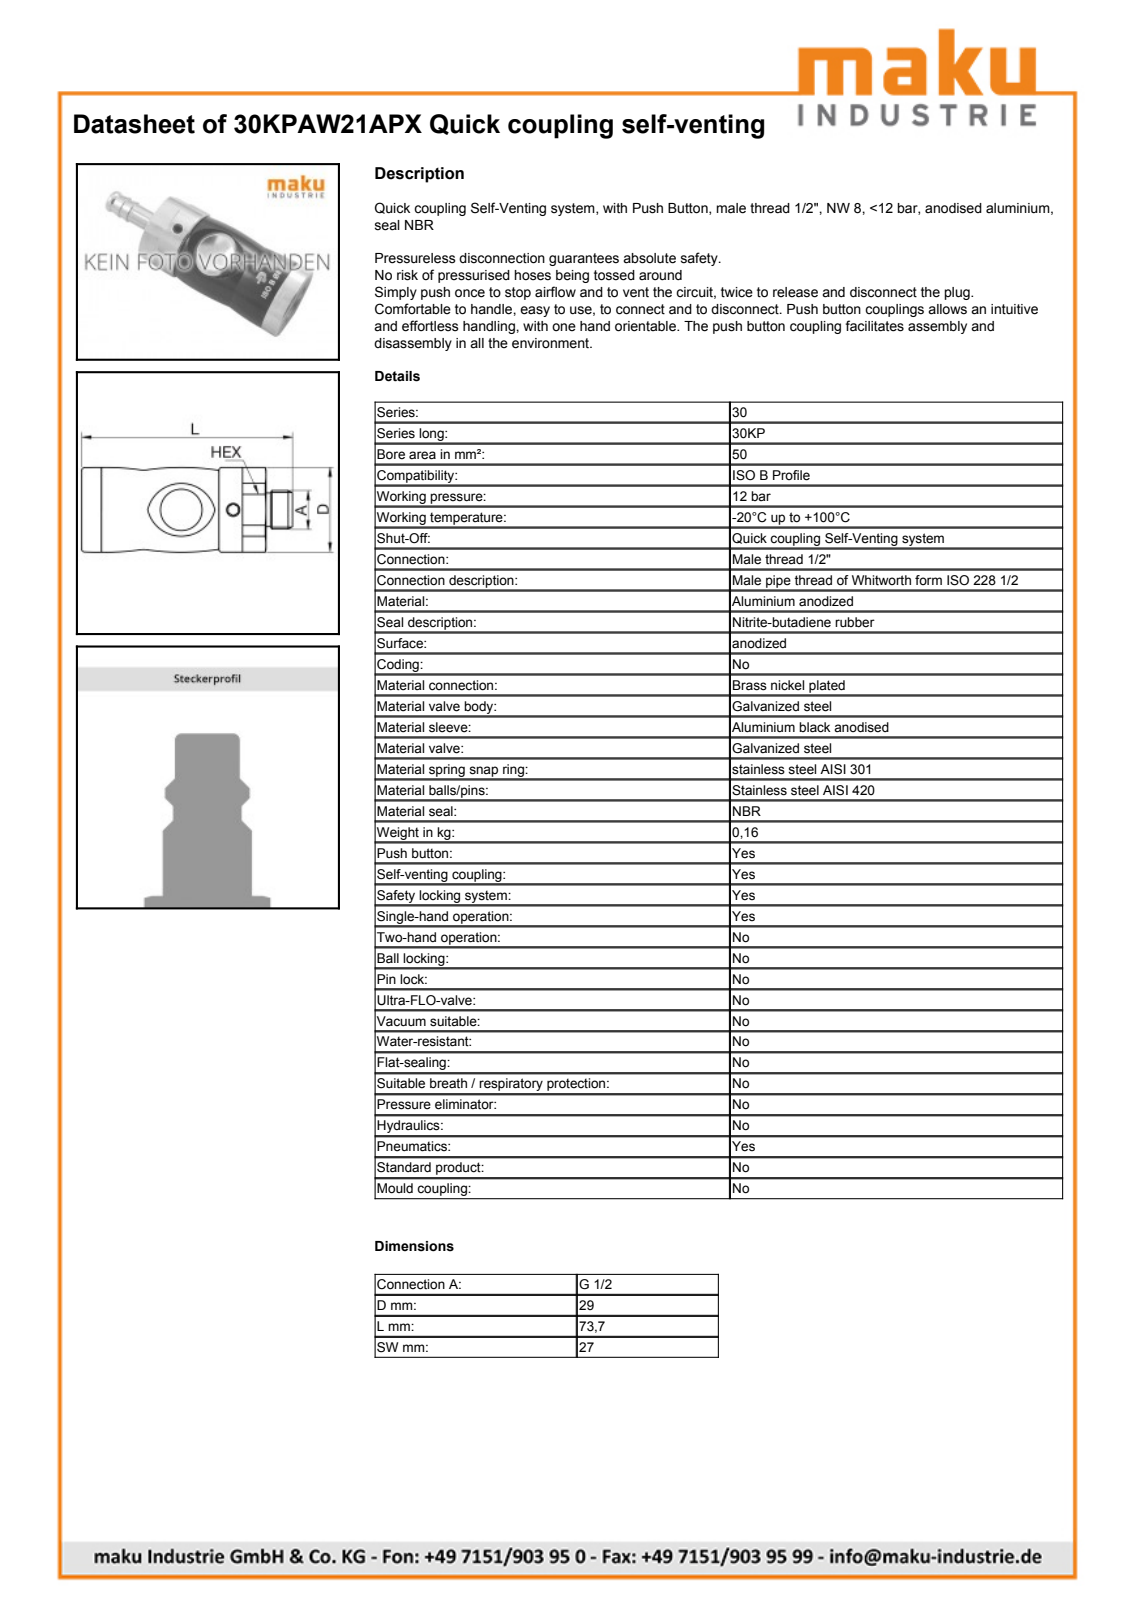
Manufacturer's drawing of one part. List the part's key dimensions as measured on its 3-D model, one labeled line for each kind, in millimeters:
Part name (STEP PRODUCT): 30KPAW21APX
STEP written by: Autodesk Inventor 2019 (CONFIG_CONTROL_DESIGN)
Units: millimetres
Bodies: 42 solids, 247 faces (74 planar, 77 cylindrical, 96 other)
Overall size (bounding box): 73.7 × 29.04 × 29.04
Volume: 46 878 mm³ · Surface area: 28 015 mm²
Round holes (diameter × count): ⌀3.5 ×1, ⌀8.5 ×1, ⌀11.2 ×1, ⌀12.2 ×1, ⌀14 ×1, ⌀14 ×1, ⌀15.3 ×1, ⌀16 ×1, ⌀17.5 ×1, ⌀18.1 ×1, ⌀20.61 ×1, ⌀20.7 ×1
Round bosses / shafts (diameter × count): ⌀29.01 ×1, ⌀26 ×1, ⌀24.65 ×1, ⌀24.5 ×1, ⌀24 ×1, ⌀21 ×1, ⌀20.5 ×1, ⌀18.2 ×1
Partial cylindrical surfaces — rounded edges, fillets, slot ends (radius × count): R2.5 ×4, R7.1 ×2
Main face-to-face distances: 27, 46.7, 6.7, 15, 40, 55, 61.7, 12, 67, 73.7
Hole centre spacings: 17.65
